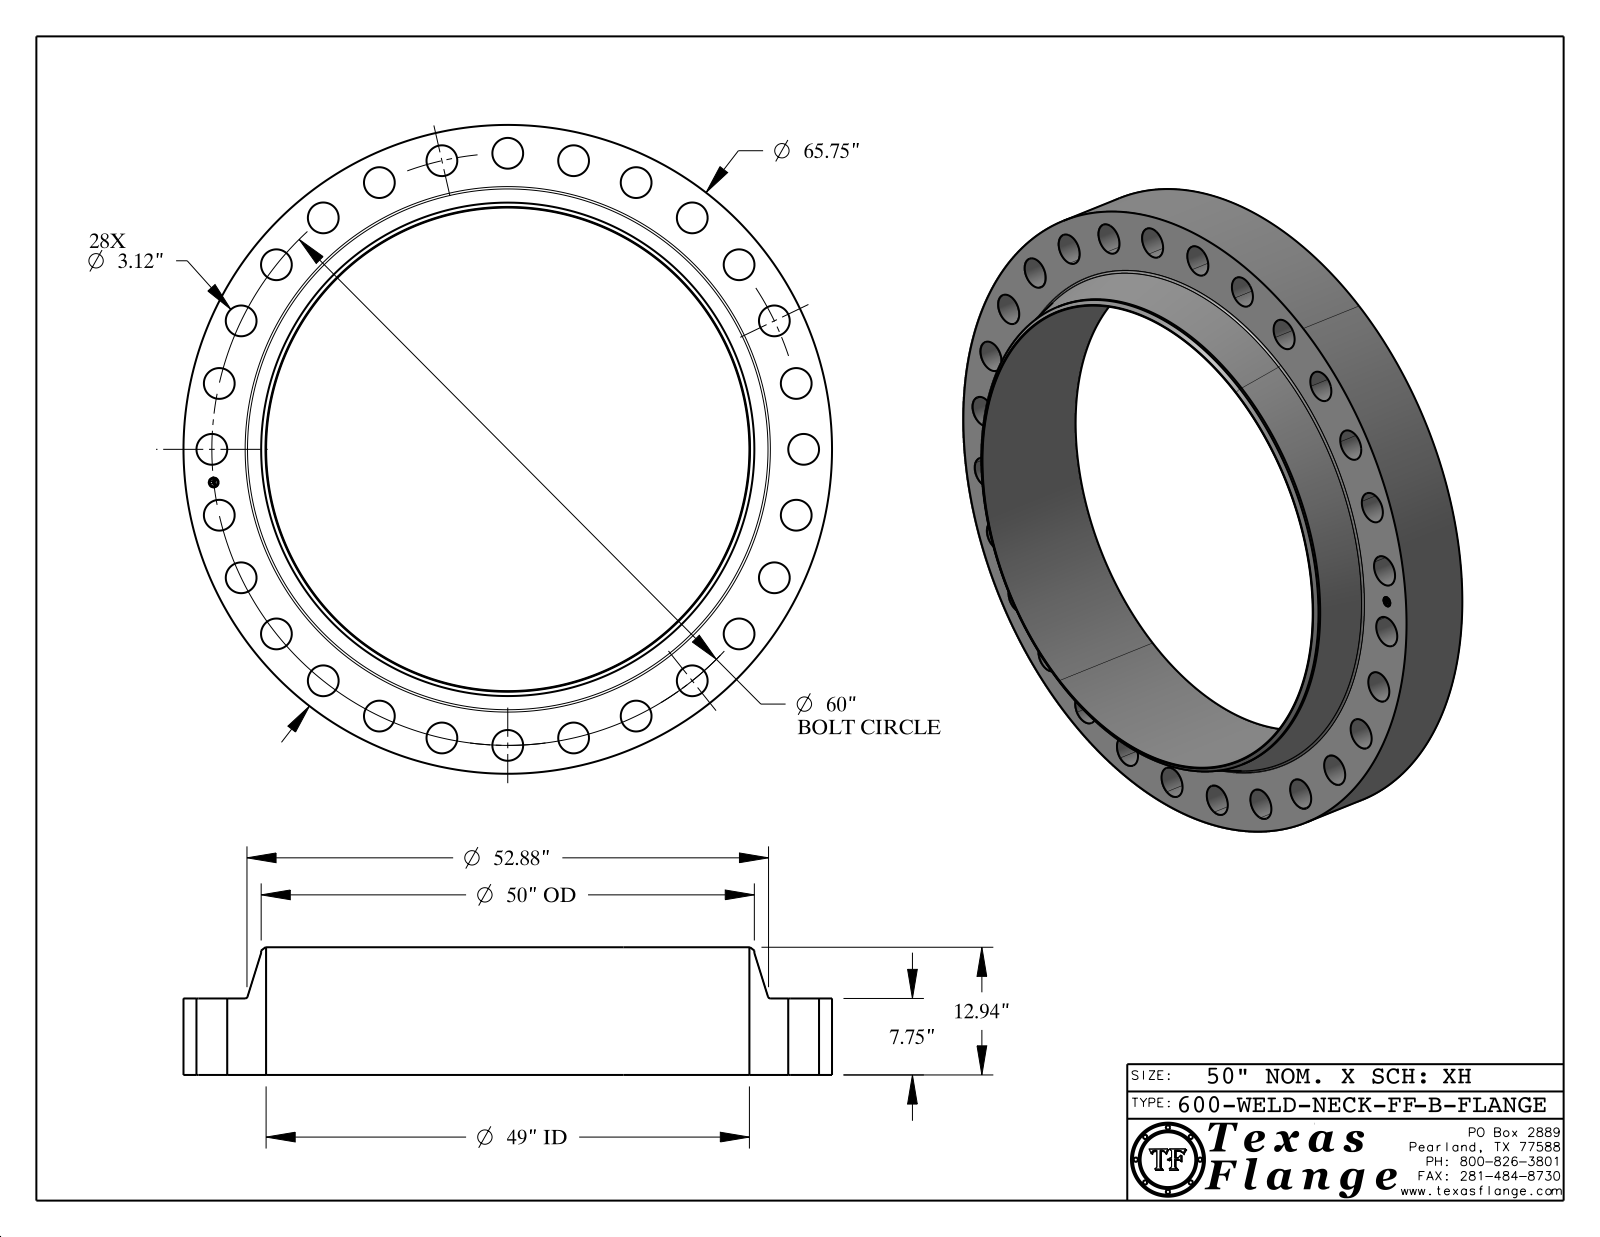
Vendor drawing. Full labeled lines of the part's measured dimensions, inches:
Part name (STEP PRODUCT): 600-WELD-NECK-FF, Series B
STEP written by: CATIA V5 STEP AP214 (AUTOMOTIVE_DESIGN)
Units: inches
Bodies: 1 solid, 456 faces (368 planar, 82 cylindrical, 6 other)
Overall size (bounding box): 65.75 × 65.75 × 12.94
Volume: 10 966 in³ · Surface area: 8 906 in²
Round holes (diameter × count): ⌀3.12 ×28, ⌀1 ×1, ⌀49 ×1
Round bosses / shafts (diameter × count): ⌀0.061 ×8, ⌀65.75 ×1, ⌀50 ×1, ⌀0.788 ×1
Main face-to-face distances: 7.75, 12.94, 5.19, 0.015, 7.735, 5.205, 0.298, 0.293, 0.054, 0.193
Hole centre spacings: 30, 26.033, 37.409, 50.804, 56.633, 59.623, 31.922, 13.351
